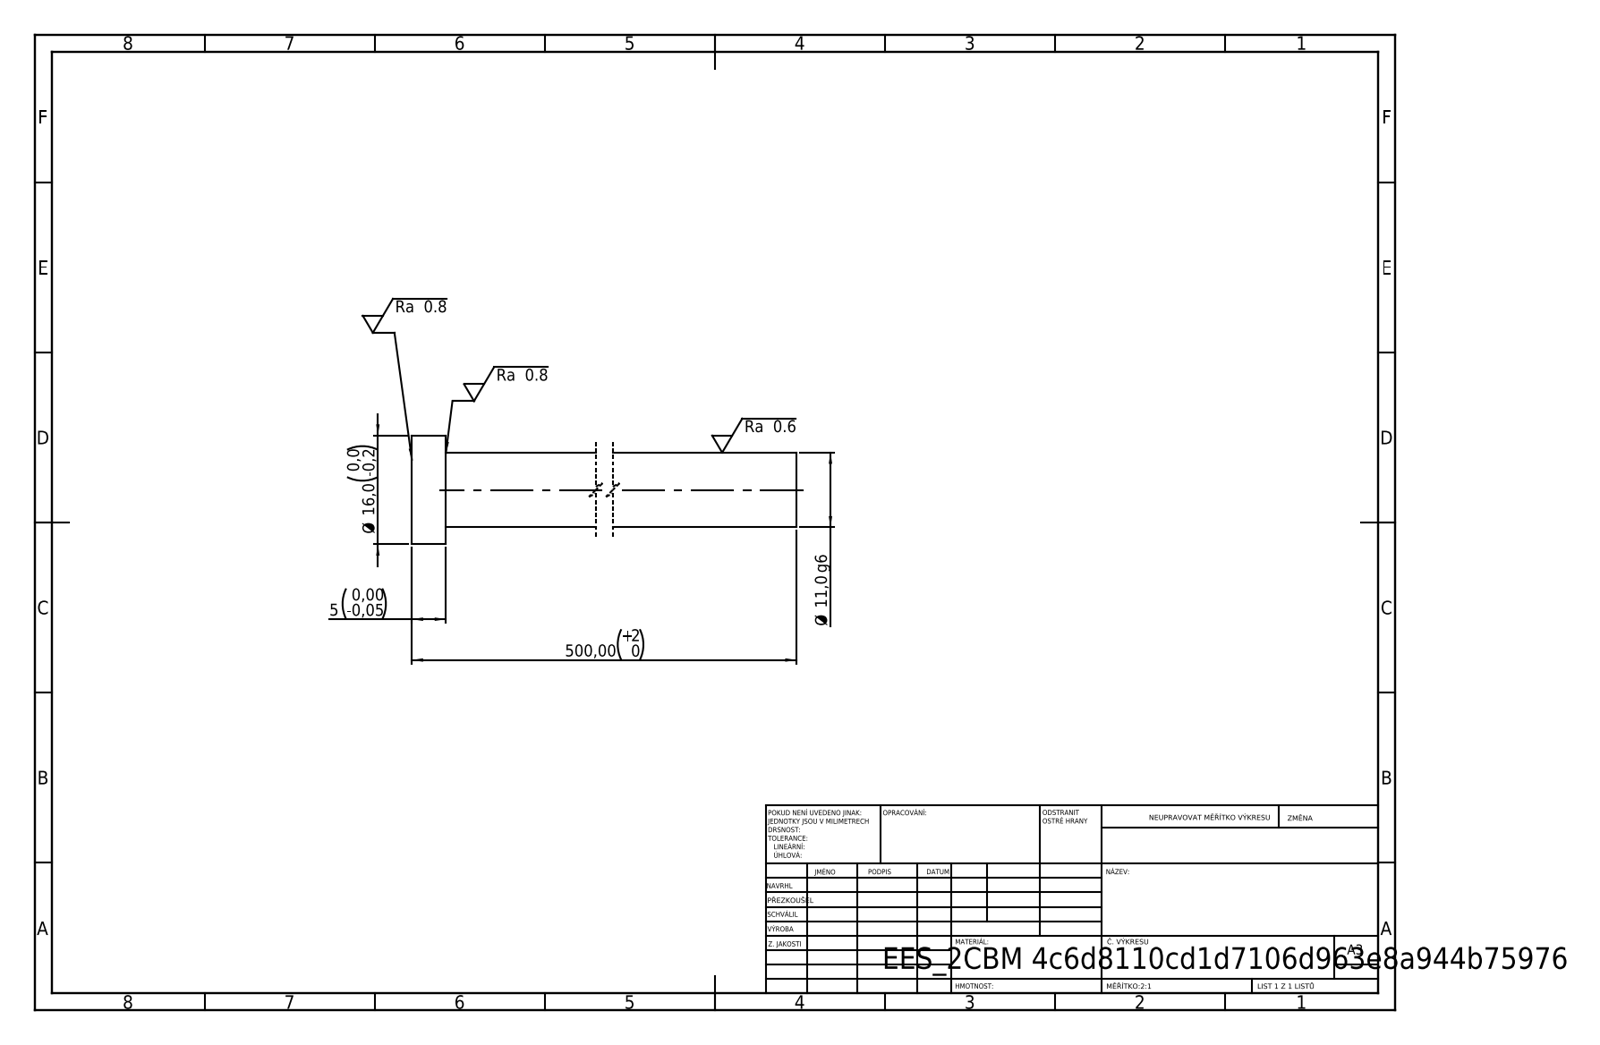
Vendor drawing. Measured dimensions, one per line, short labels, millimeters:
written by: SolidWorks 2019 (CONFIG_CONTROL_DESIGN)
unit: mm
bodies: 1 solid, 7 faces (3 planar, 4 cylindrical, 0 other)
size: 500 × 16 × 16
volume: 48 047 mm³; area: 17 759 mm²
bosses: 1× ⌀16, 1× ⌀11
face distances: 5, 500, 495
